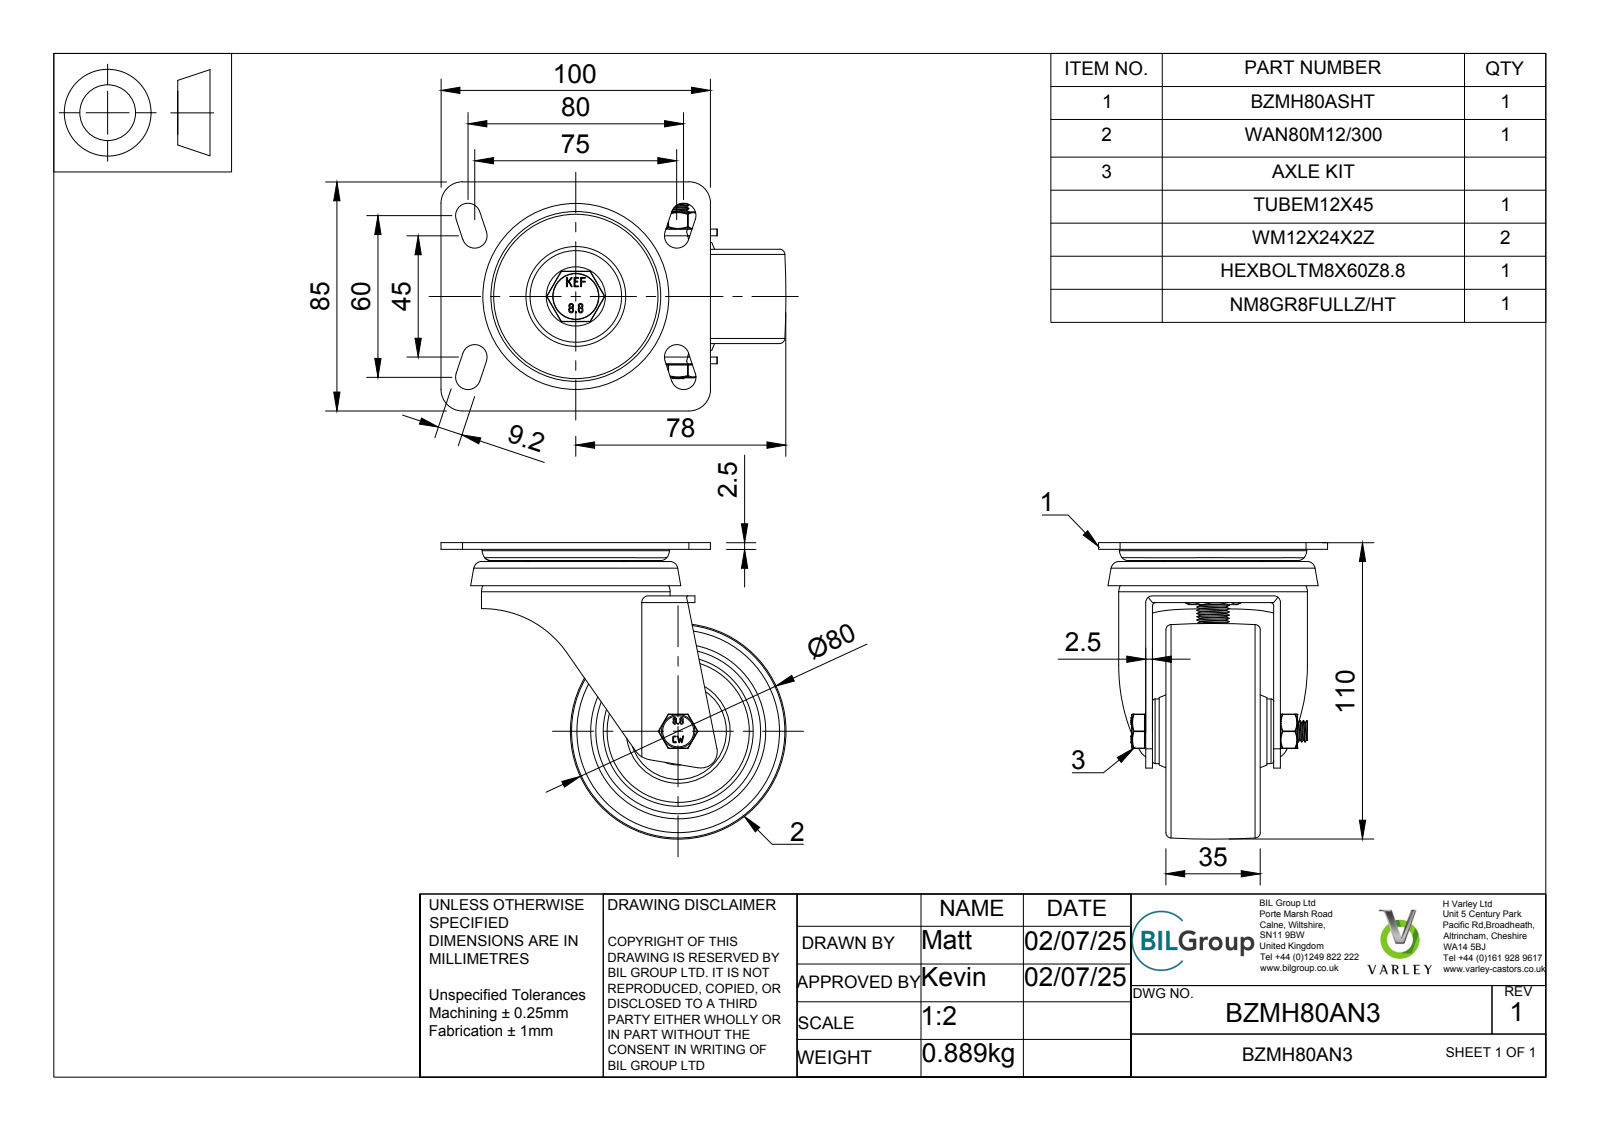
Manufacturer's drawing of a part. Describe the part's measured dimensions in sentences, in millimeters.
The part is named "BZMH80AN3 v3; BZMH80ASHT v1; PRESSED STEEL TOP PLATE; PRESSED STEEL TOP PLATE Geometry (+6 more)". Its 3-D file was written by "Autodesk Translation Framework v14.10.0.0 (AUTOMOTIVE_DESIGN)". It is 52 solids with 551 faces: 170 planar, 152 cylindrical and 229 other. Overall it measures 128 by 110 by 85 millimeters. Its volume is 222 522 cubic millimeters and its surface area 100 362 square millimeters. Round holes: 2 of diameter 0.66, 1 of diameter 8, 1 of diameter 8.2, 1 of diameter 12, 1 of diameter 12.5, 1 of diameter 13, 1 of diameter 22.68, 1 of diameter 65. Round bosses or shafts: 1 of diameter 70, 1 of diameter 69.5, 1 of diameter 56, 1 of diameter 46, 1 of diameter 24, 1 of diameter 18, 1 of diameter 17, 1 of diameter 12. Partial cylindrical surfaces (rounded edges, fillets, slot ends): 18 of radius 0.25, 8 of radius 4.6, 5 of radius 8, 4 of radius 0.33, 4 of radius 0.64, 4 of radius 1.25, 2 of radius 0.63, 2 of radius 0.64. The main face-to-face distances are 2.5, 9.25, 6.75, 5, 42.5, 19, 16.5, 40, 45, 2.25. The hole center spacings are 4.65, 2.49.
